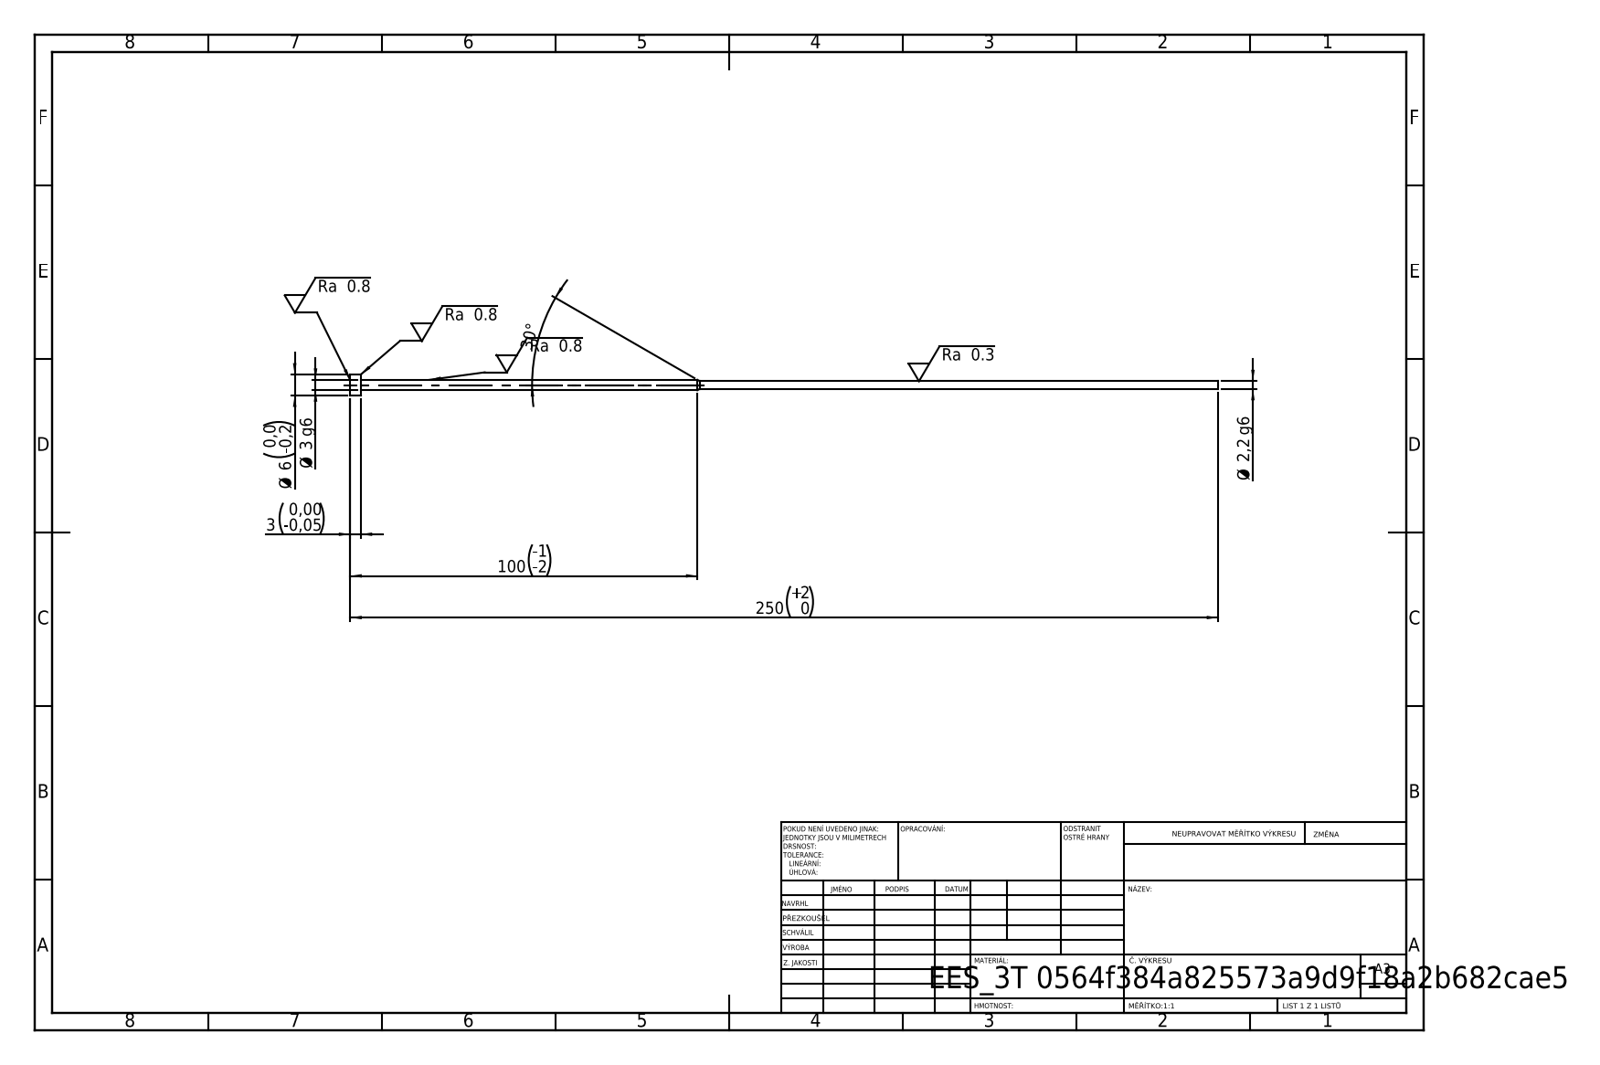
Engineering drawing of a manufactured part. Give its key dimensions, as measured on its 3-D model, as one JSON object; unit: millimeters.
{"step_written_by": "SolidWorks 2019 (CONFIG_CONTROL_DESIGN)", "units": "millimeters", "bodies": {"solids": 1, "faces": 11, "planar": 3, "cylindrical": 6, "other": 2}, "overall_size": [250, 6, 6], "volume_mm3": 1342, "surface_area_mm2": 2063, "round_bosses_or_shafts": [[6, 1], [3, 1], [2.2, 1]], "face_to_face_distances": [3, 247, 250]}
